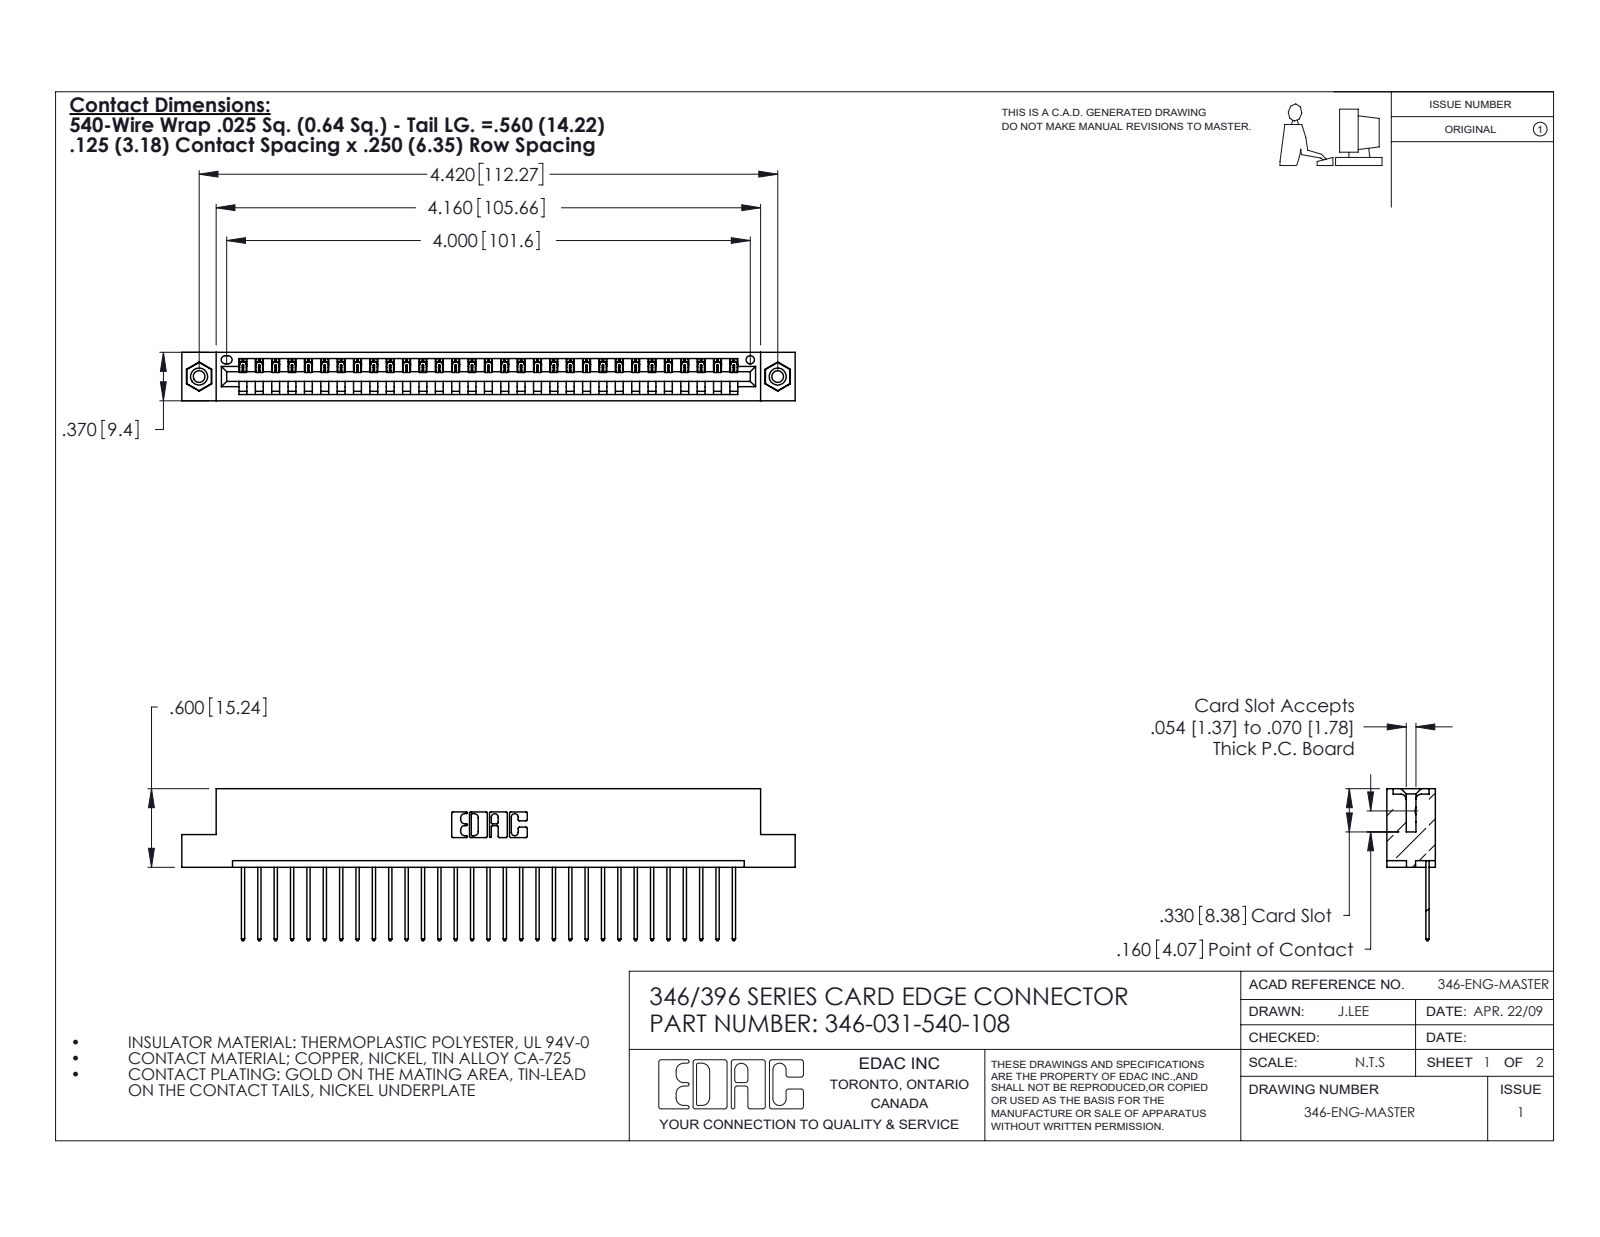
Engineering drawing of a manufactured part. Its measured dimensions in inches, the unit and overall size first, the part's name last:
Units: inches
Overall size (bounding box): 4.685 × 1.16 × 0.37
Round holes (diameter × count): ⌀0.089 ×2, ⌀0.125 ×2, ⌀0.156 ×2, ⌀0.064 ×1
Round bosses / shafts (diameter × count): ⌀0.155 ×2
Partial cylindrical surfaces — rounded edges, fillets, slot ends (radius × count): R0.006 ×62, R0.01 ×62, R0.01 ×22, R0.007 ×6, R0.031 ×6, R0.026 ×3, R0.031 ×2, R0.04 ×2
Main face-to-face distances: 0.048, 0.322, 0.37, 0.25, 0.072, 0.298, 0.025, 0.148, 0.222, 0.1
Hole centre spacings: 0.246, 4.212, 4.42
Volume: 0.693 in³ · Surface area: 22.31 in²
Bodies: 34 solids, 1980 faces (1348 planar, 616 cylindrical, 16 other)
Part name (STEP PRODUCT): 346 Part_Flush Mounting Lugs - 0.156 Dia-TI; 345-250-001_345-250-003-102; 346-031-540-108; 345-292-001_345-293-140
STEP written by: SolidWorks 2020 (CONFIG_CONTROL_DESIGN)
